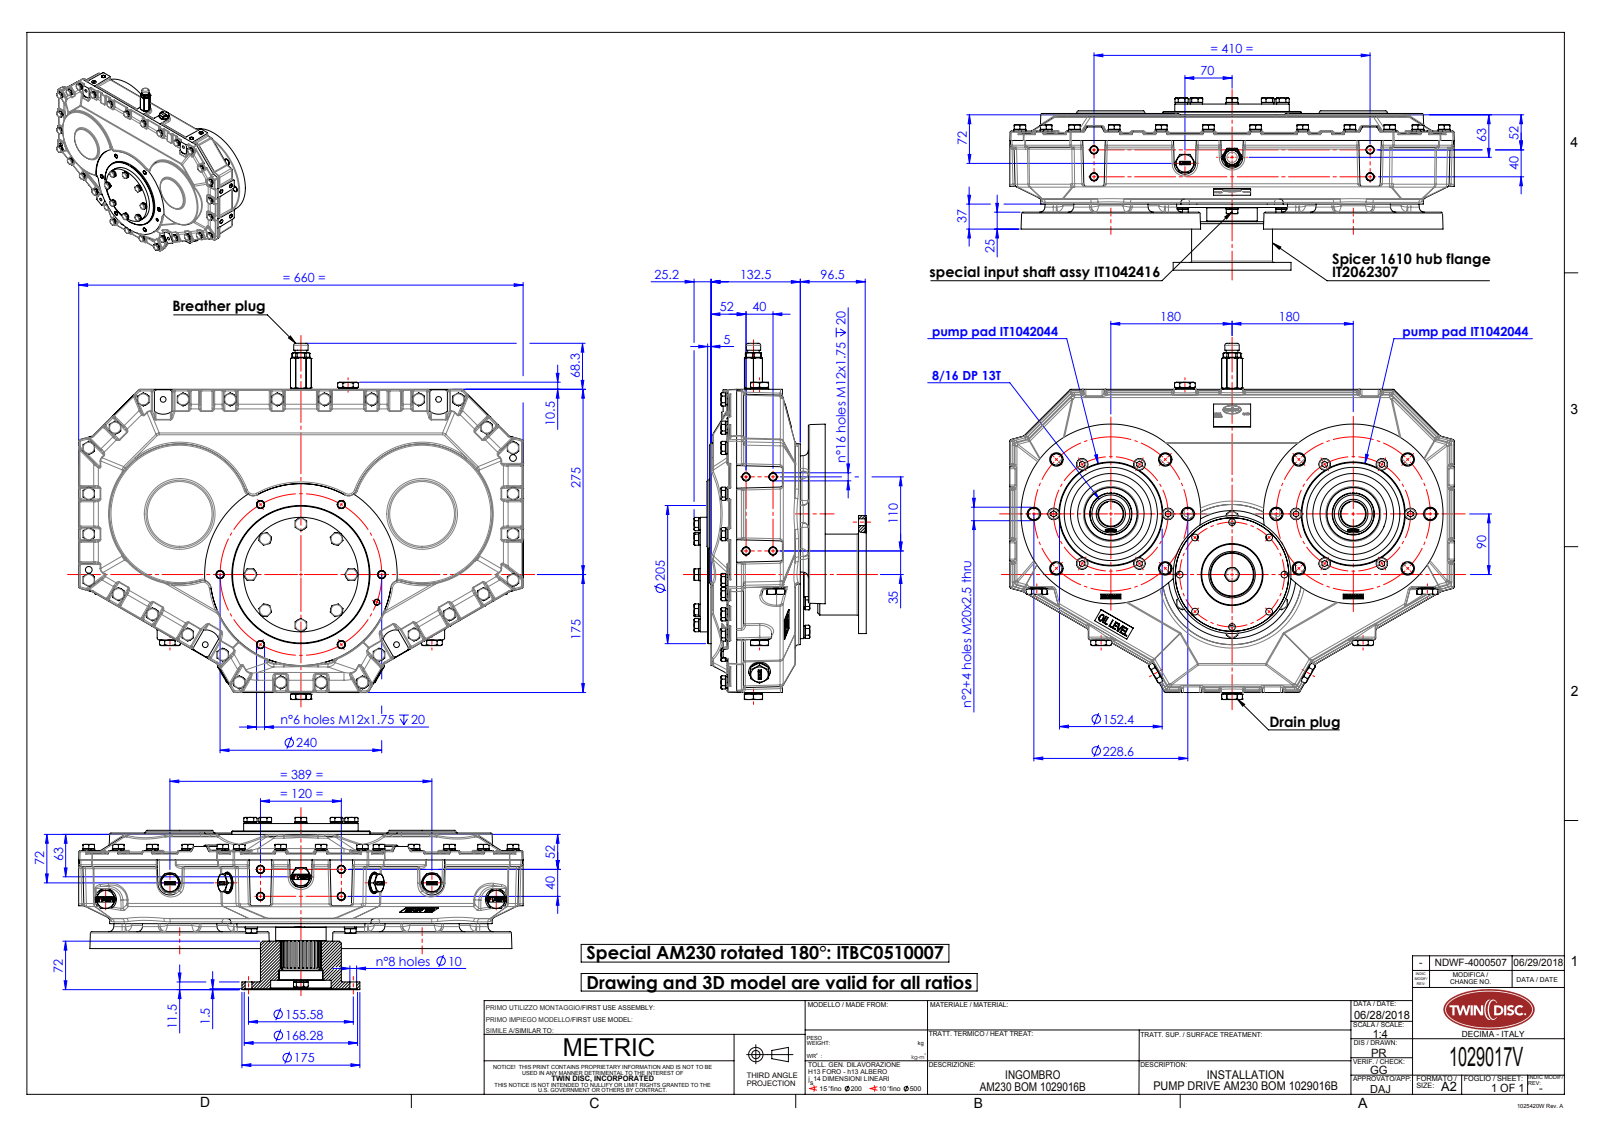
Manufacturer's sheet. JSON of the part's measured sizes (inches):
{"part_name": "IT1042044_rev00-installation; IT4588040_rev00-installation; IT2021216_rev03-installation; ITBC0510000-installation (+7 more)", "step_written_by": "SolidWorks 2015 (AUTOMOTIVE_DESIGN)", "units": "inches", "bodies": {"solids": 62, "faces": 6659, "planar": 2740, "cylindrical": 1749, "other": 2170}, "overall_size": [25.984, 20.819, 10.067], "volume_in3": 326.3, "surface_area_in2": 3500, "round_holes": [[0.402, 61], [0.413, 36], [0.335, 30], [0.433, 20], [0.472, 19], [0.669, 12], [0.689, 12], [0.394, 10], [0.827, 5], [0.733, 4], [0.728, 3], [0.787, 3]], "round_bosses_or_shafts": [[0.394, 54], [0.713, 42], [0.638, 42], [0.787, 12], [0.63, 12], [1.063, 5], [1.022, 5], [0.815, 5]], "partial_cylinders_radius": [[0.079, 199], [0.118, 103], [0.098, 78], [0.197, 74], [0.018, 58], [0.315, 24], [0.512, 18], [0.059, 14]], "face_to_face_distances": [0.197, 0.748, 1.457, 0.984, 5.295, 4.921, 1.024, 0.472, 0.118, 0.551], "hole_center_spacings": [2.26, 4.724, 5.456, 1.575, 8.183, 0.889, 2.022, 2.622]}
